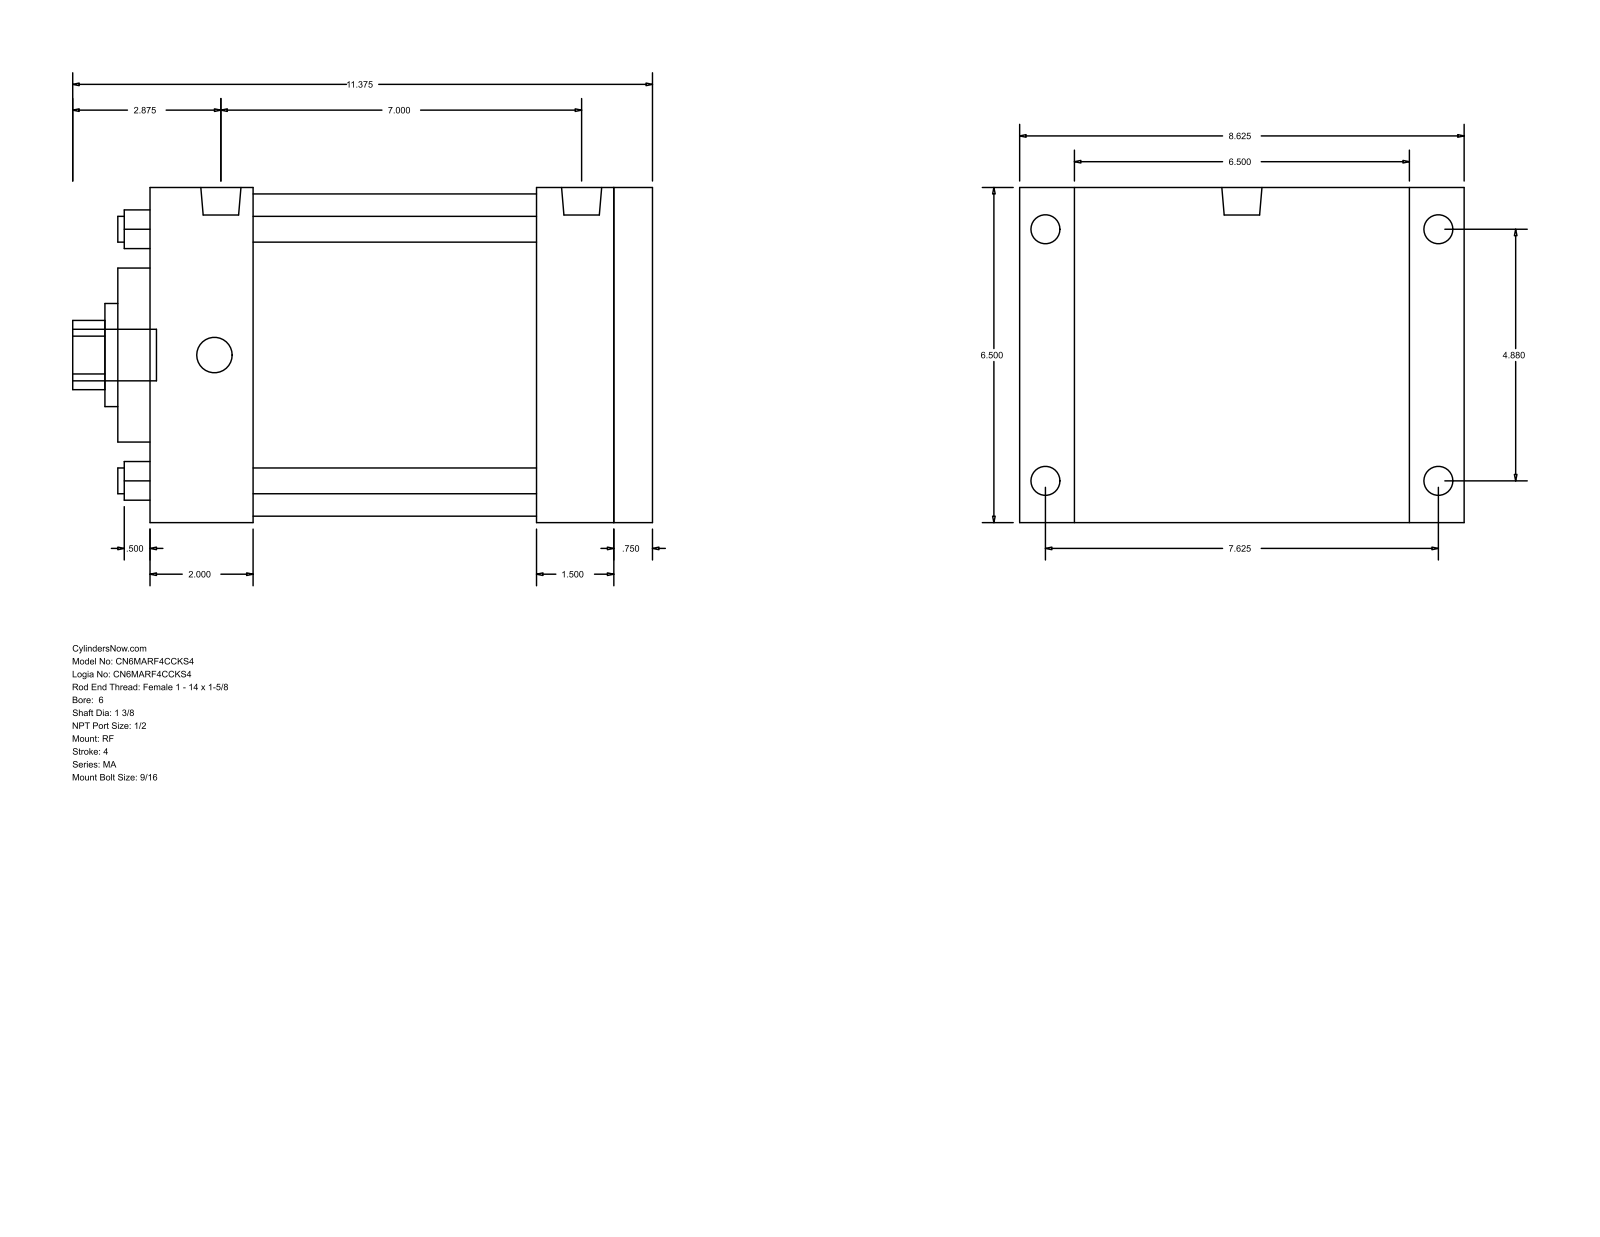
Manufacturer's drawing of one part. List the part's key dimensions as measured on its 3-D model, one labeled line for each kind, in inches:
Part name (STEP PRODUCT): MA_RF__0600_1.375
STEP written by: GSSL Pune (CONFIG_CONTROL_DESIGN)
Units: inches
Bodies: 0 solids, 94 faces (65 planar, 29 cylindrical, 0 other)
Overall size (bounding box): 11.375 × 8.625 × 6.5
Round holes (diameter × count): ⌀0.5 ×4, ⌀1.375 ×1, ⌀2 ×1, ⌀3.375 ×1, ⌀6.25 ×1
Round bosses / shafts (diameter × count): ⌀0.687 ×4, ⌀0.563 ×4, ⌀0.778 ×2, ⌀1 ×1
Partial cylindrical surfaces — rounded edges, fillets, slot ends (radius × count): R0.672 ×1
Main face-to-face distances: 6.5, 9.875, 0.75, 9.125, 1.5, 2, 7.125, 7.875, 7.625, 5.625
Hole centre spacings: 3.451, 4.88, 6.902
